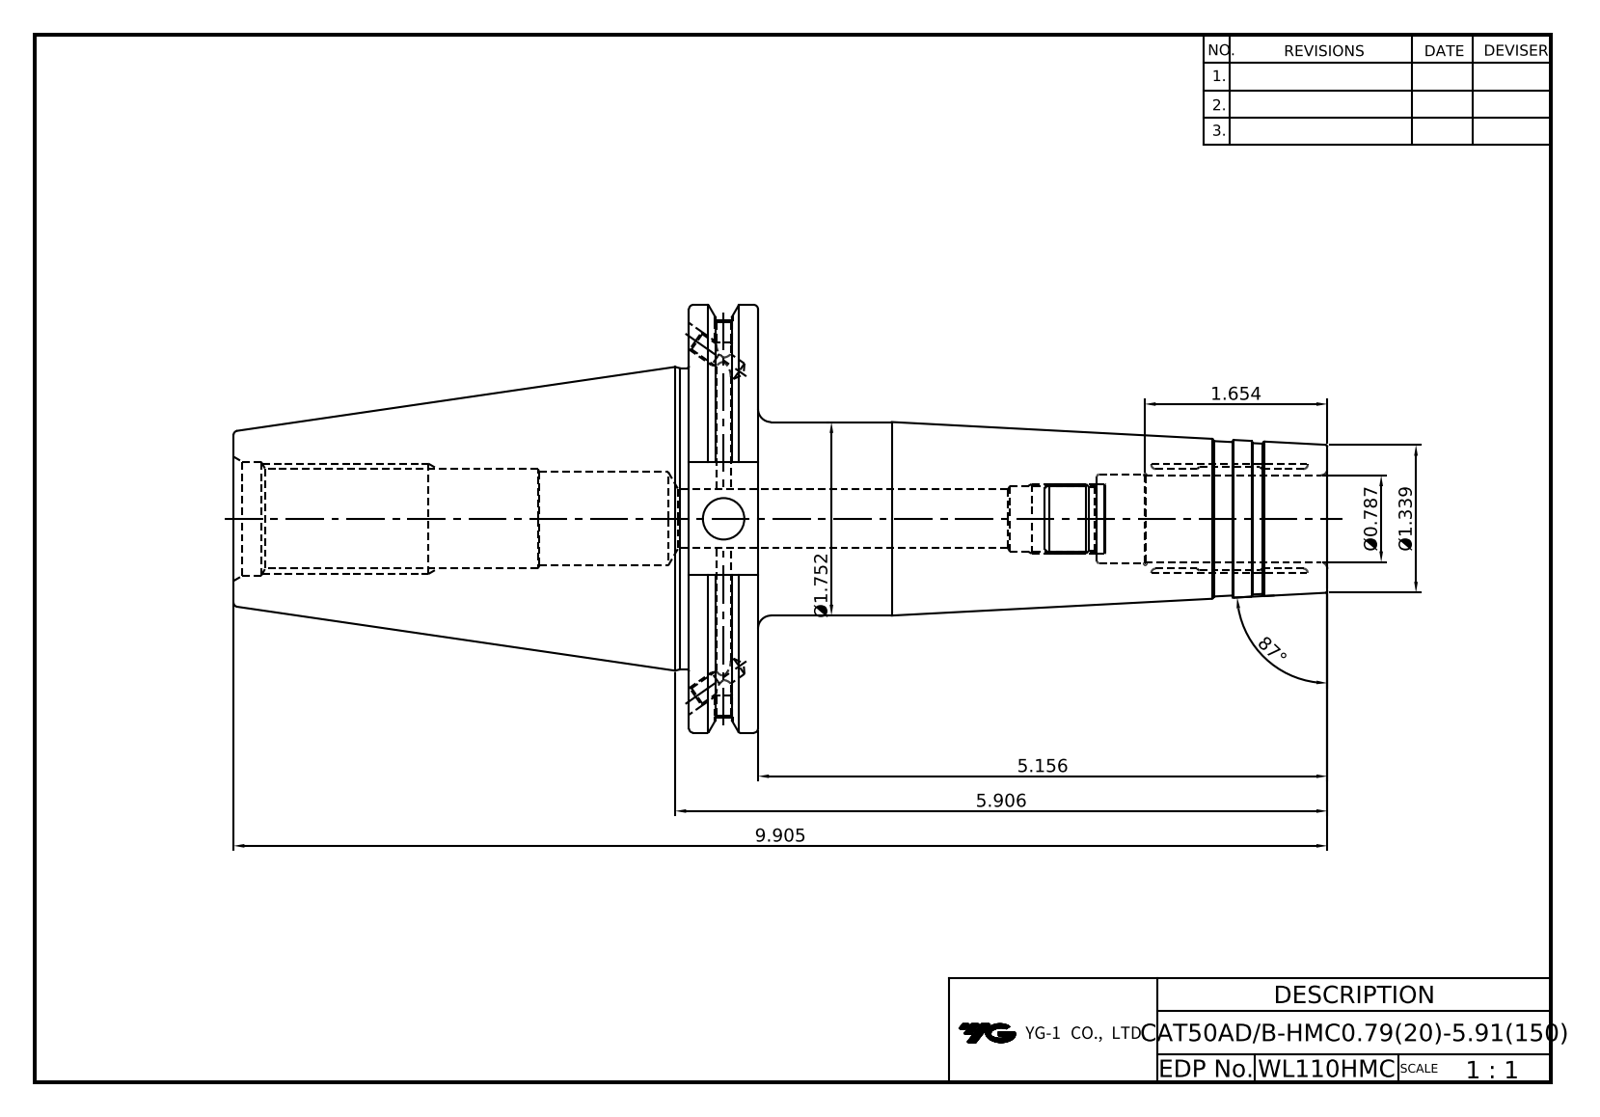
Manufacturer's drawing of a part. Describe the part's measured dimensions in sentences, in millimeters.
The part is named "LO-CAT50ADB-HMC20-150". Its 3-D file was written by "Autodesk Inventor 2025 (AUTOMOTIVE_DESIGN)". It is 1 solid with 105 faces: 37 planar, 28 cylindrical and 40 other. Overall it measures 251.6 by 98.42 by 94.69 millimeters. Its volume is 464 066 cubic millimeters and its surface area 67 169 square millimeters. Round holes: 2 of diameter 3.24, 2 of diameter 4.13, 2 of diameter 4.2, 2 of diameter 5, 1 of diameter 9.53, 1 of diameter 13.5, 1 of diameter 14.92, 1 of diameter 20, 1 of diameter 20.4, 1 of diameter 21.5, 1 of diameter 21.97, 1 of diameter 26.2. Round bosses or shafts: 1 of diameter 98.42, 1 of diameter 91.29, 1 of diameter 69.25, 1 of diameter 44.5. The main face-to-face distances are 15.88, 104.77, 120.65, 251.6, 146.83, 130.95, 73.03, 25.9, 110.82, 6.05.
